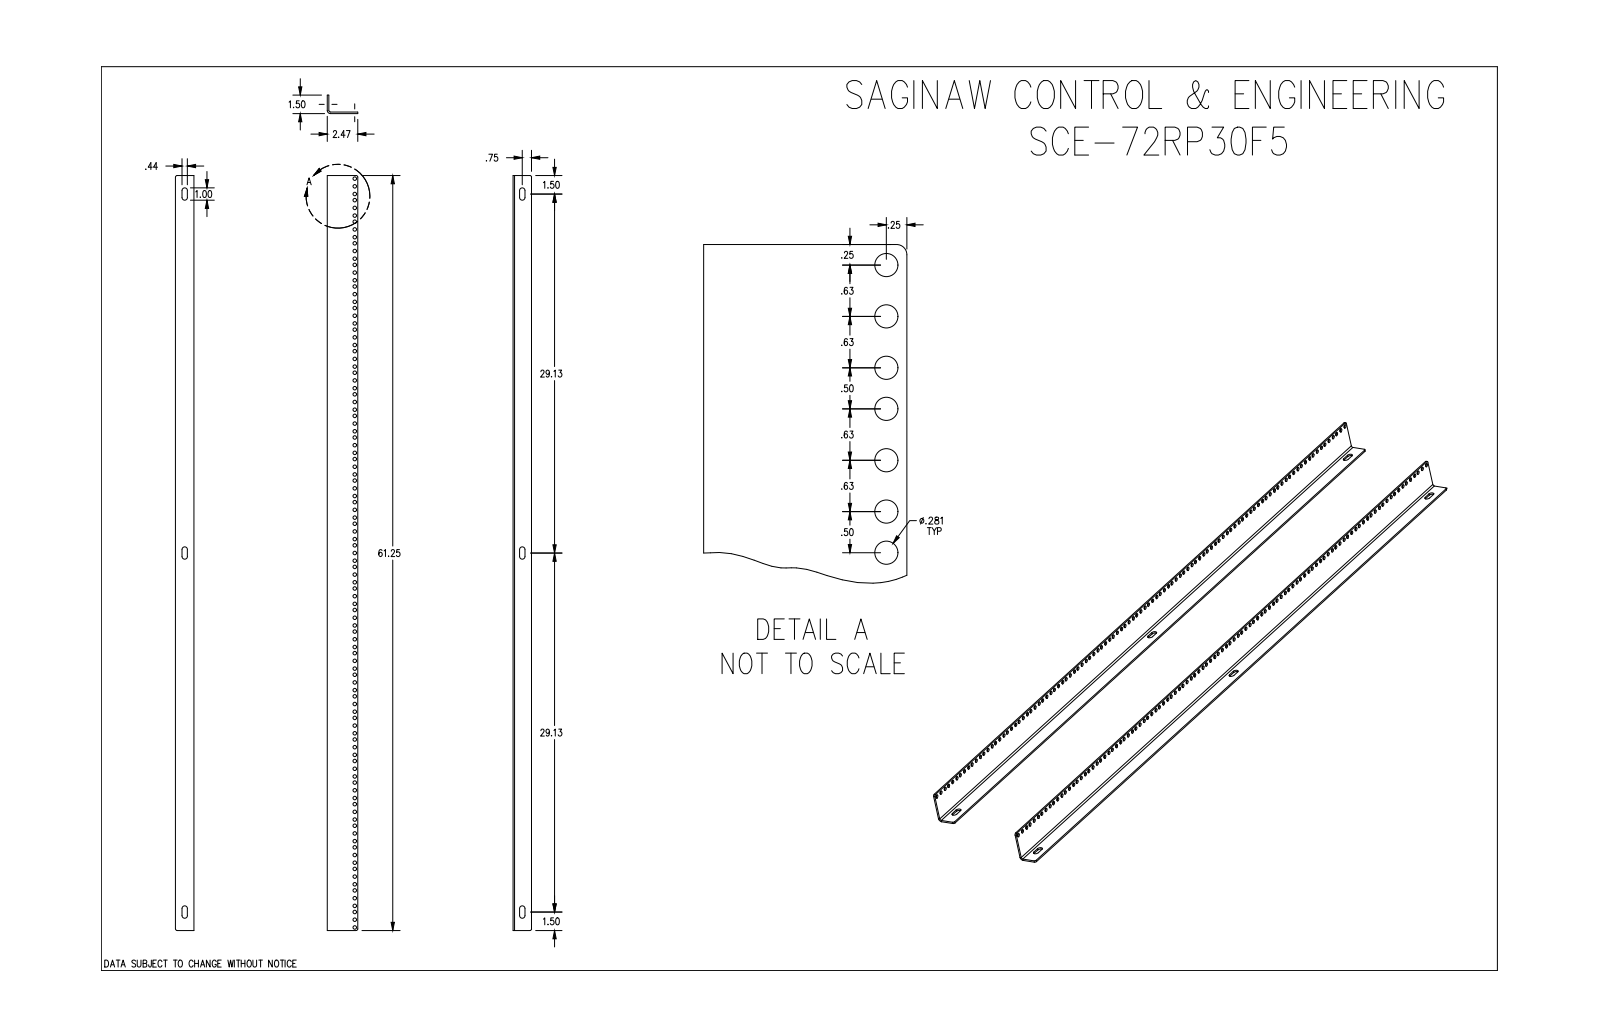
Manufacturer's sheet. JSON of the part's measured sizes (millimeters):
{"part_name": "SCE-72RP30F5", "step_written_by": "SolidWorks 2019 (CONFIG_CONTROL_DESIGN)", "units": "millimeters", "bodies": {"solids": 1, "faces": 240, "planar": 18, "cylindrical": 222, "other": 0}, "overall_size": [1555.8, 62.8, 38.1], "volume_mm3": 457000, "surface_area_mm2": 306500, "round_holes": [[7.1, 105]], "partial_cylinders_radius": [[5.6, 6], [3.3, 3], [3.2, 2], [6.4, 1]], "face_to_face_distances": [3.2, 59.7, 62.8, 38.1, 34.9, 1555.8, 13.5, 24.6, 10.3, 21.4], "hole_center_spacings": [44.5, 88.9, 133.4, 177.8, 222.3, 15.9, 15.9, 31.8]}
